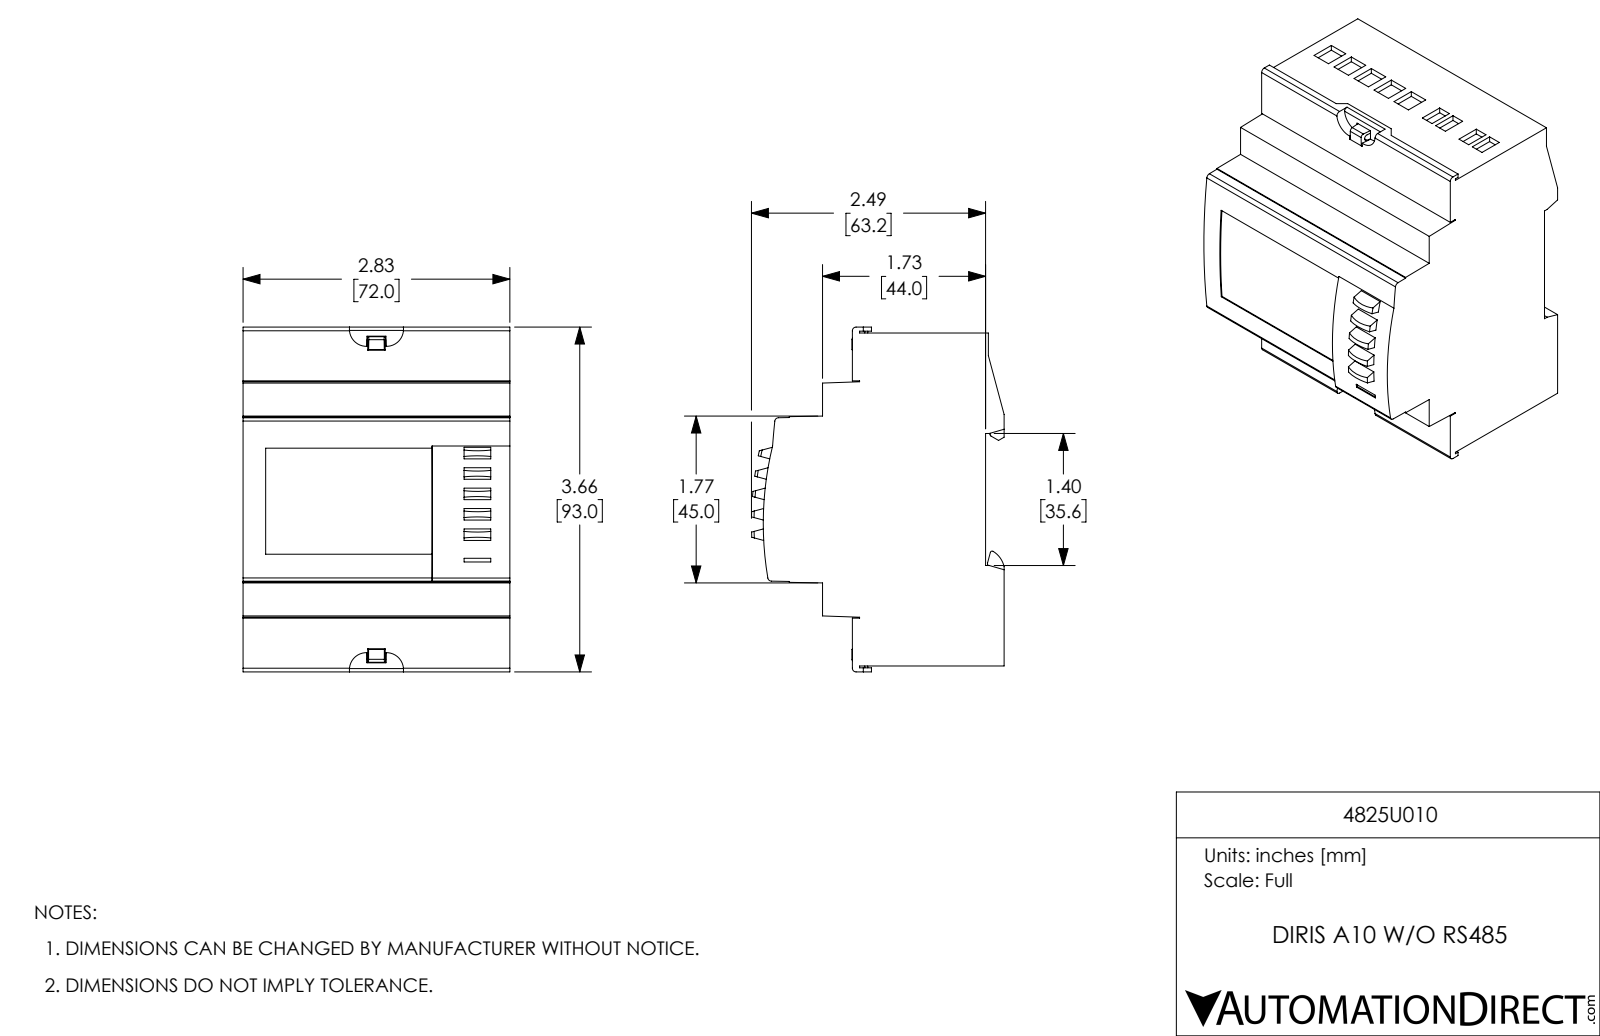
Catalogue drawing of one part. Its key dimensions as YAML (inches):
part_name: "4825U010"
step_written_by: "SolidWorks 2017 (AUTOMOTIVE_DESIGN)"
units: inches
bodies: {solids: 1, faces: 532, planar: 373, cylindrical: 128, other: 31}
overall_size: [3.661, 2.835, 2.684]
volume: 19.95
surface_area: 56.72
round_holes:
  - {diameter: 0.198, count: 7}
  - {diameter: 0.161, count: 6}
  - {diameter: 0.198, count: 4}
round_bosses_or_shafts:
  - {diameter: 0.187, count: 11}
  - {diameter: 0.15, count: 6}
partial_cylinders:
  - {radius: 0.039, count: 5}
  - {radius: 0.035, count: 4}
  - {radius: 0.129, count: 4}
  - {radius: 0.129, count: 4}
  - {radius: 0.181, count: 4}
  - {radius: 0.22, count: 4}
  - {radius: 0.26, count: 4}
  - {radius: 0.3, count: 4}
face_to_face_distances: [2.835, 3.535, 0.197, 1.415, 1.612, 1.929, 1.732, 0.317, 0.03, 0.167]
hole_center_spacings: [0.25, 0.3, 0.5, 0.2, 0.6, 0.75, 0.55, 0.9]
